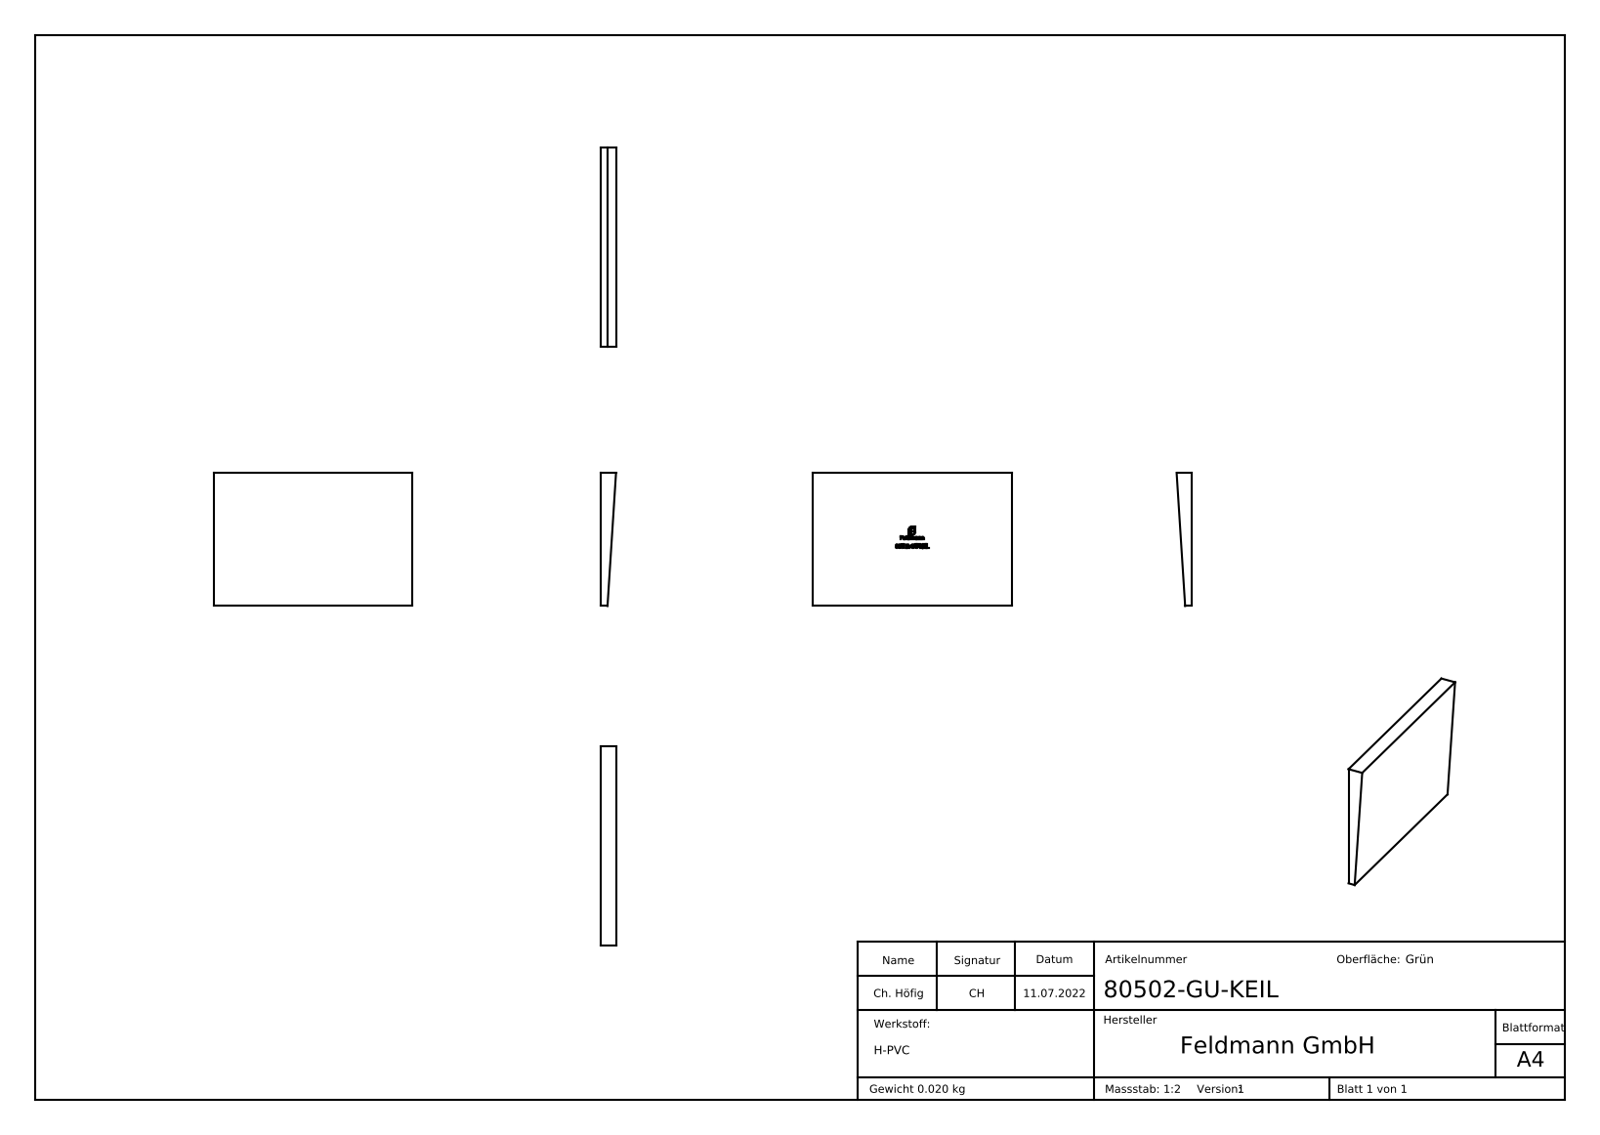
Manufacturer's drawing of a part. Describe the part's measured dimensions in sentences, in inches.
The part is named "80502-GU-KEIL". Its 3-D file was written by "SolidWorks 2018 (CONFIG_CONTROL_DESIGN)". It is 1 solid with 307 faces: 174 planar, 0 cylindrical and 133 other. Overall it measures 2.941 by 1.969 by 0.228 inches. Its volume is 0.957 cubic inches and its surface area 13.24 square inches. The main face-to-face distances are 2.941, 1.969, 0.013, 0.087, 0.077, 0.035, 0.052, 0.858, 1.11, 0.241.
